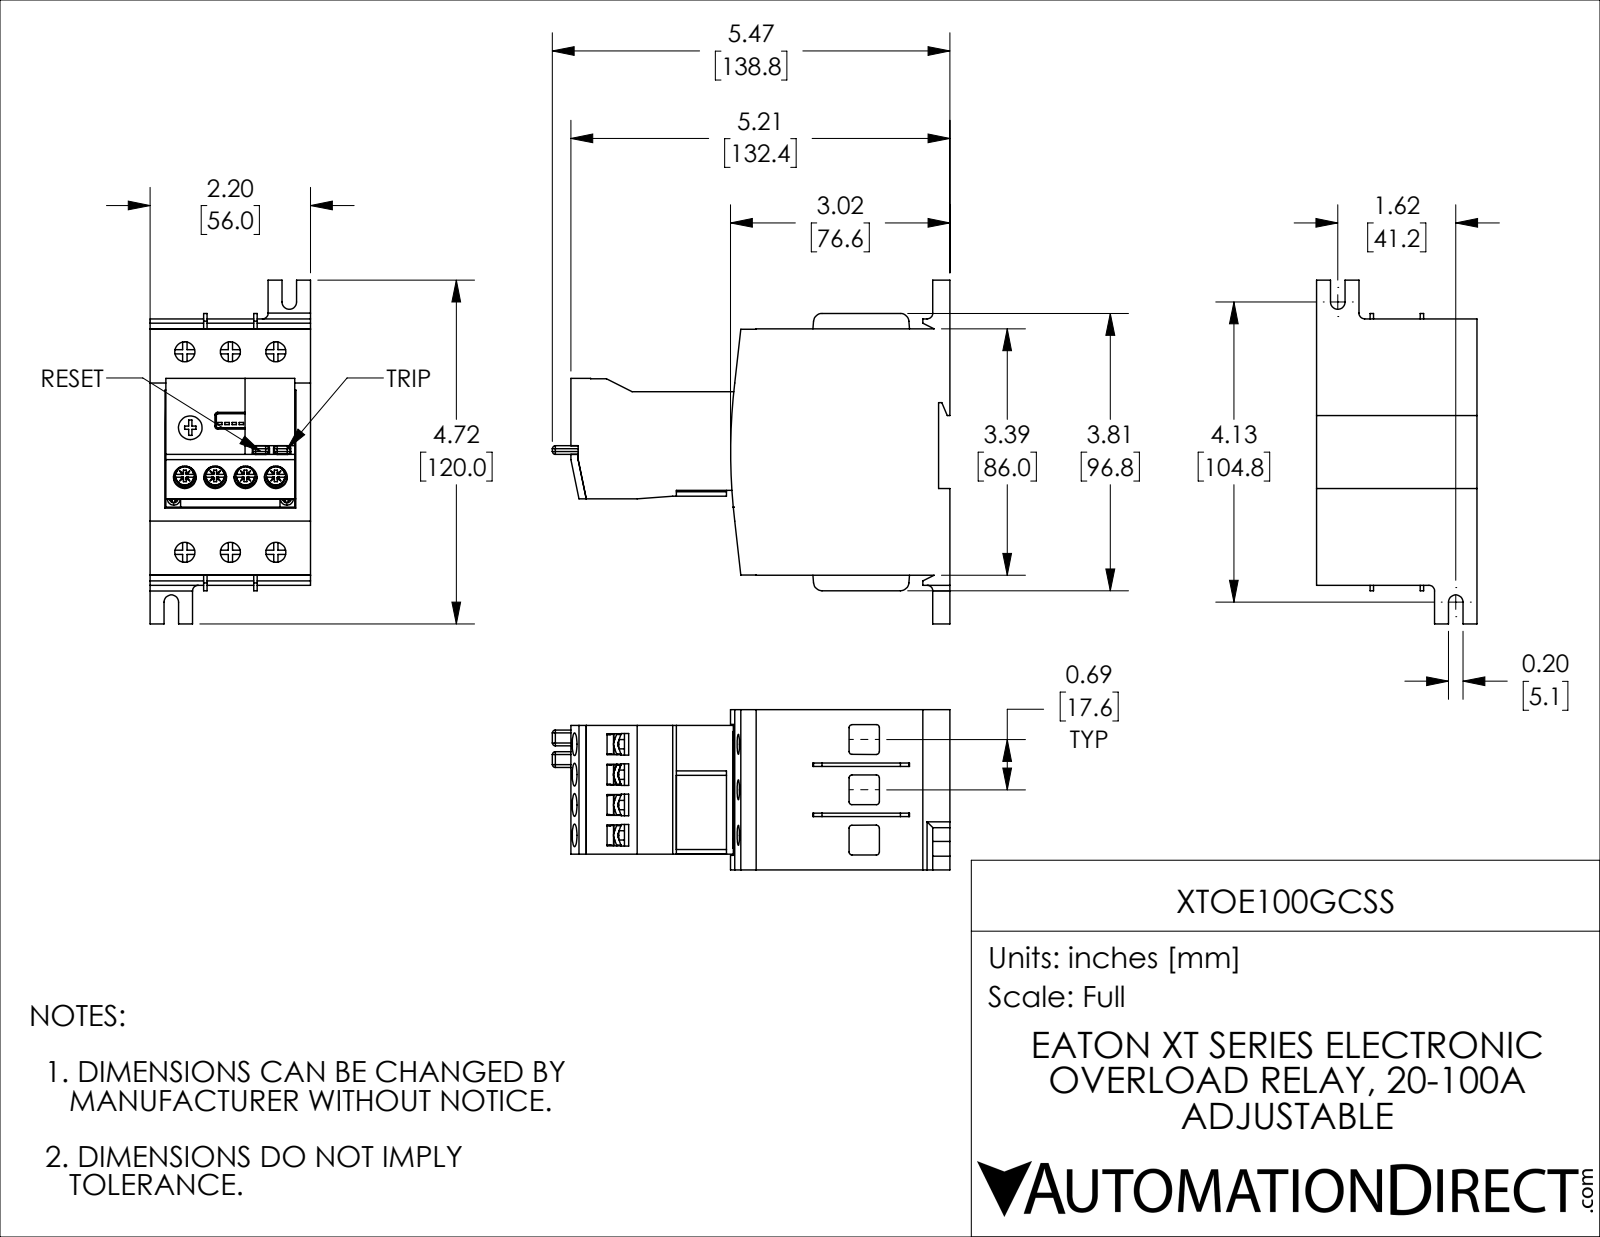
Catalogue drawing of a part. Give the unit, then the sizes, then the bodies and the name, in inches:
Units: inches
Overall size (bounding box): 5.467 × 4.724 × 2.205
Round holes (diameter × count): ⌀0.276 ×6, ⌀0.14 ×4, ⌀0.268 ×4, ⌀0.314 ×4, ⌀0.086 ×2, ⌀0.126 ×2
Round bosses / shafts (diameter × count): ⌀0.134 ×4, ⌀0.128 ×4, ⌀0.11 ×4, ⌀0.098 ×4, ⌀0.177 ×2, ⌀0.325 ×1, ⌀0.181 ×1
Partial cylindrical surfaces — rounded edges, fillets, slot ends (radius × count): R0.02 ×24, R0.039 ×14, R0.079 ×12, R0.118 ×6, R0.014 ×2, R0.062 ×2, R0.1 ×2, R0.031 ×1
Main face-to-face distances: 2.205, 0.217, 1.988, 2.746, 3.386, 1.772, 2.524, 0.862, 1.358, 0.157
Hole centre spacings: 0.417, 0.835, 1.051, 1.072, 1.705, 1.717, 2.826, 0.35
Volume: 27.32 in³ · Surface area: 93.78 in²
Bodies: 31 solids, 1045 faces (690 planar, 189 cylindrical, 166 other)
Part name (STEP PRODUCT): XTOE100GCSS
STEP written by: SolidWorks 2018 (AUTOMOTIVE_DESIGN)
